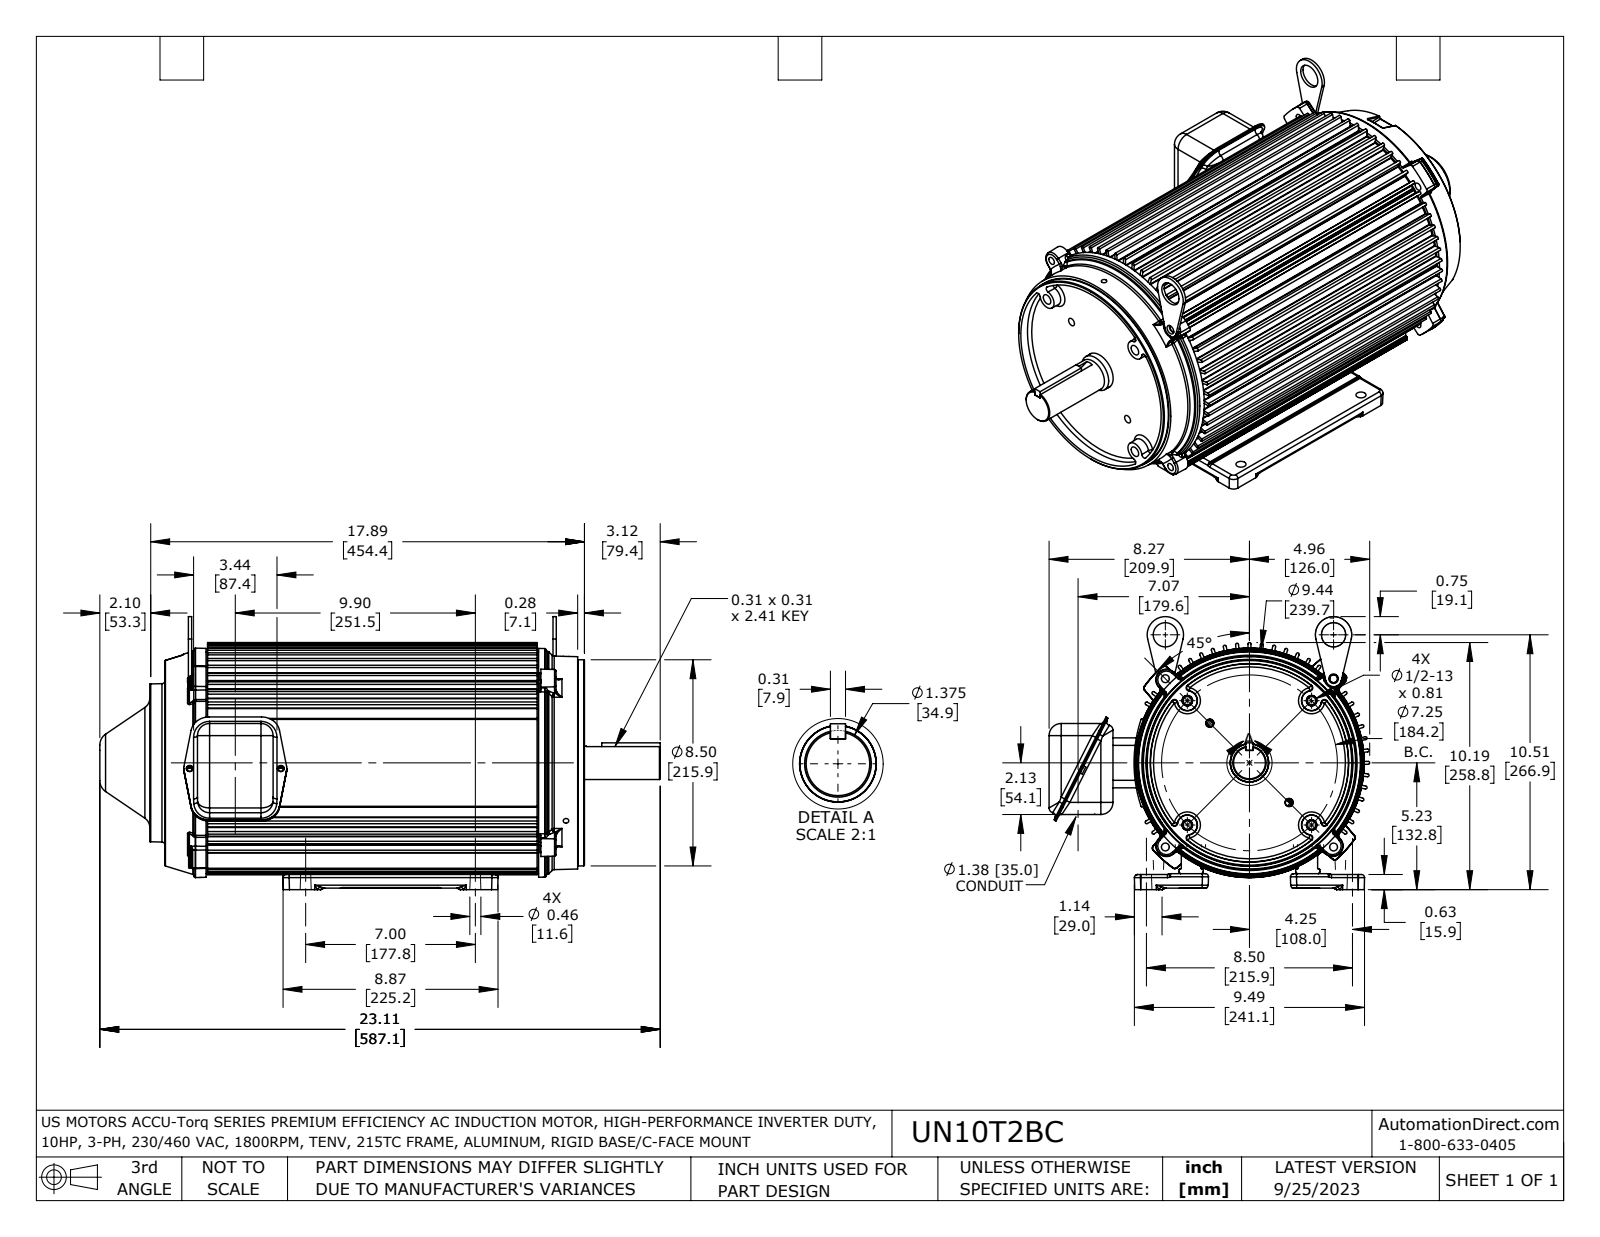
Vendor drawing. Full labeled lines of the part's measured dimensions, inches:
Part name (STEP PRODUCT): UN10T2BC b fxt
STEP written by: SolidWorks 2021 (AUTOMOTIVE_DESIGN)
Units: inches
Bodies: 5 solids, 2382 faces (445 planar, 756 cylindrical, 1181 other)
Overall size (bounding box): 23.115 × 13.226 × 11.317
Volume: 1 310 in³ · Surface area: 1 237 in²
Round holes (diameter × count): ⌀0.313 ×4, ⌀0.328 ×4, ⌀0.406 ×4, ⌀0.436 ×4, ⌀0.107 ×2, ⌀0.227 ×2, ⌀0.281 ×2, ⌀0.391 ×2, ⌀1 ×2, ⌀0.173 ×1, ⌀1.191 ×1, ⌀1.38 ×1
Round bosses / shafts (diameter × count): ⌀0.323 ×2, ⌀9.866 ×1, ⌀9.131 ×1, ⌀8.5 ×1, ⌀6.5 ×1, ⌀4.5 ×1, ⌀1.573 ×1, ⌀1.375 ×1
Partial cylindrical surfaces — rounded edges, fillets, slot ends (radius × count): R0.125 ×162, R0.063 ×68, R0.1 ×61, R0.06 ×54, R0.25 ×22, R0.031 ×18, R0.5 ×18, R0.118 ×15
Main face-to-face distances: 16.613, 0.9, 17.513, 0.315, 0.822, 0.078, 16.691, 0.034, 0.585, 0.237
Hole centre spacings: 4.666, 5.719, 6.1, 6.939, 0.688, 1.281, 1.969, 2.317
